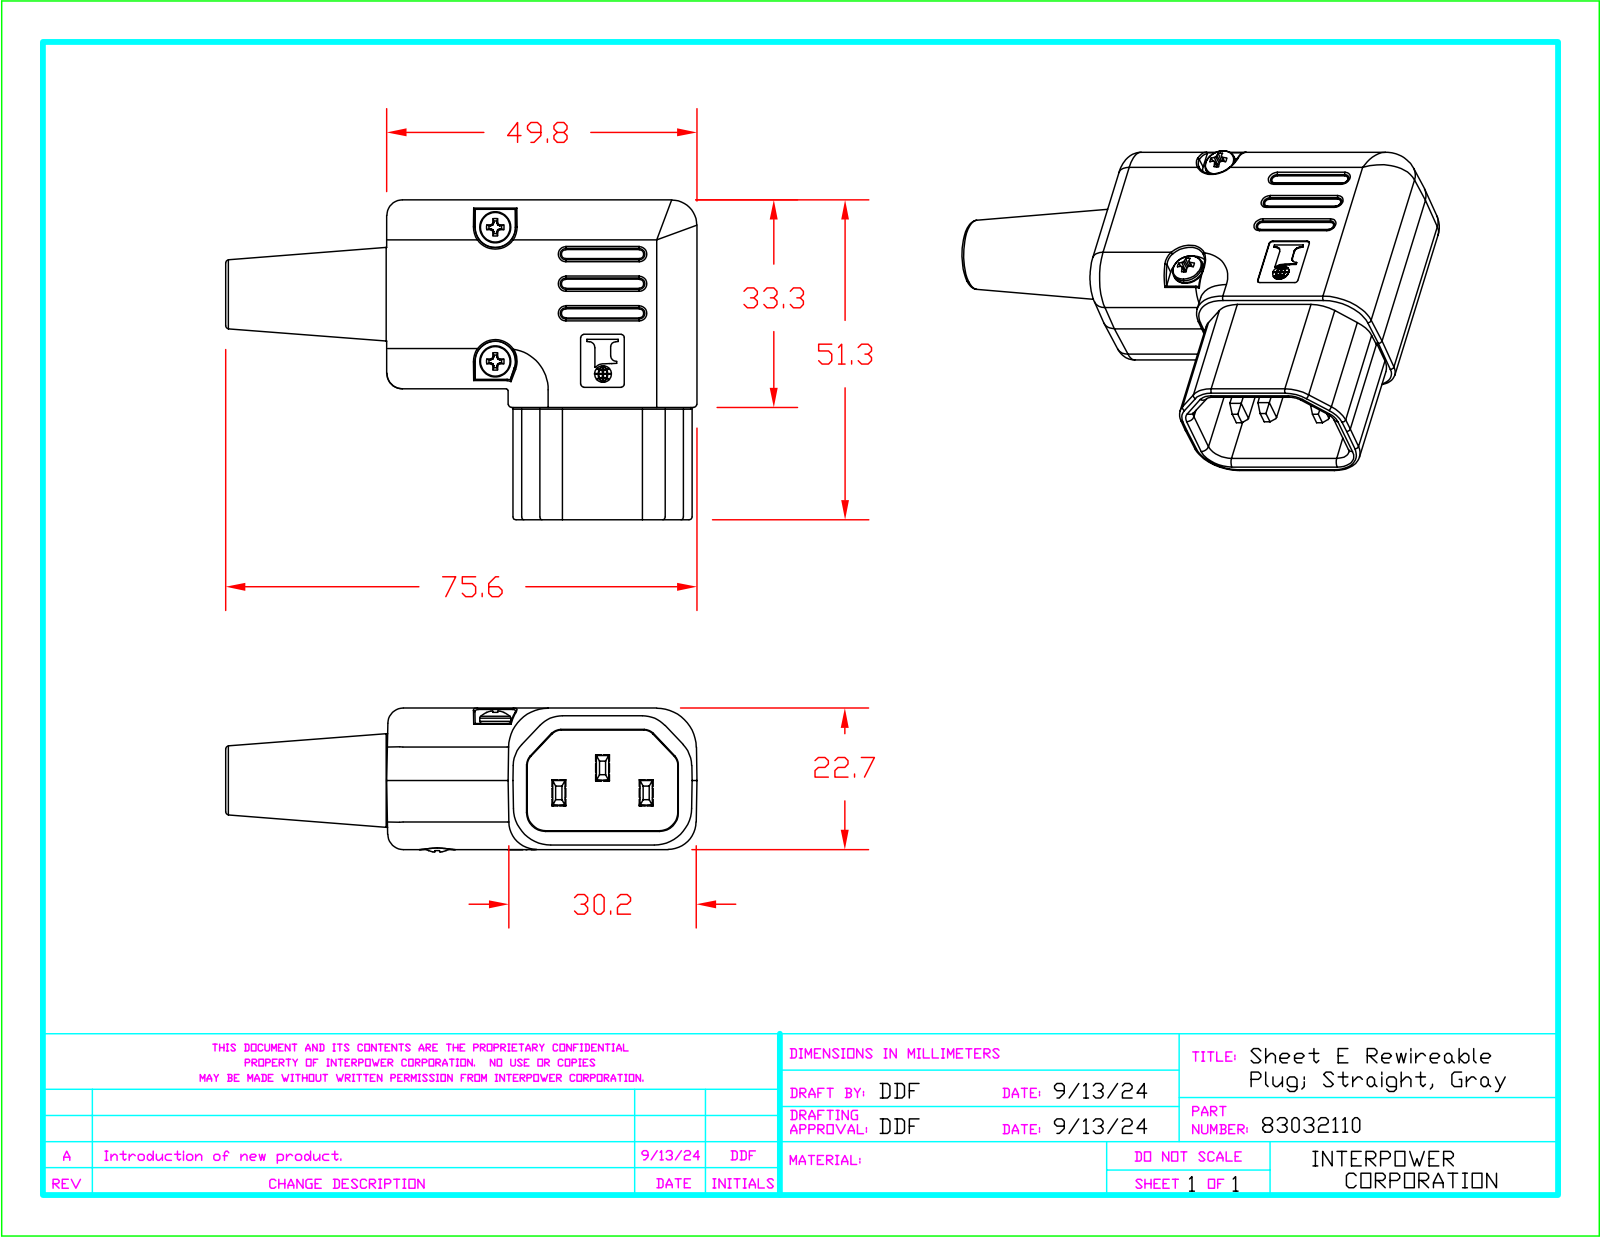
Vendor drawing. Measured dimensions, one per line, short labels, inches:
name: 83032100_SHT-E_CON_ANGL_SERVICE
written by: CREO PARAMETRIC BY PTC INC, 2014500 (CONFIG_CONTROL_DESIGN)
unit: in
bodies: 1 solid, 542 faces (216 planar, 99 cylindrical, 227 other)
size: 2.976 × 2.02 × 0.909
volume: 2.547 in³; area: 16.42 in²
bosses: 4× ⌀0.197, 1× ⌀0.591
rounds: 18× R0.02, 12× R0.008, 12× R0.014, 6× R0.039, 6× R0.098, 4× R0.079, 4× R0.177, 4× R0.197
face distances: 0.894, 0.028, 0.865, 1.959, 0.846, 0.817, 0.048, 1.193, 0.276, 1.163
